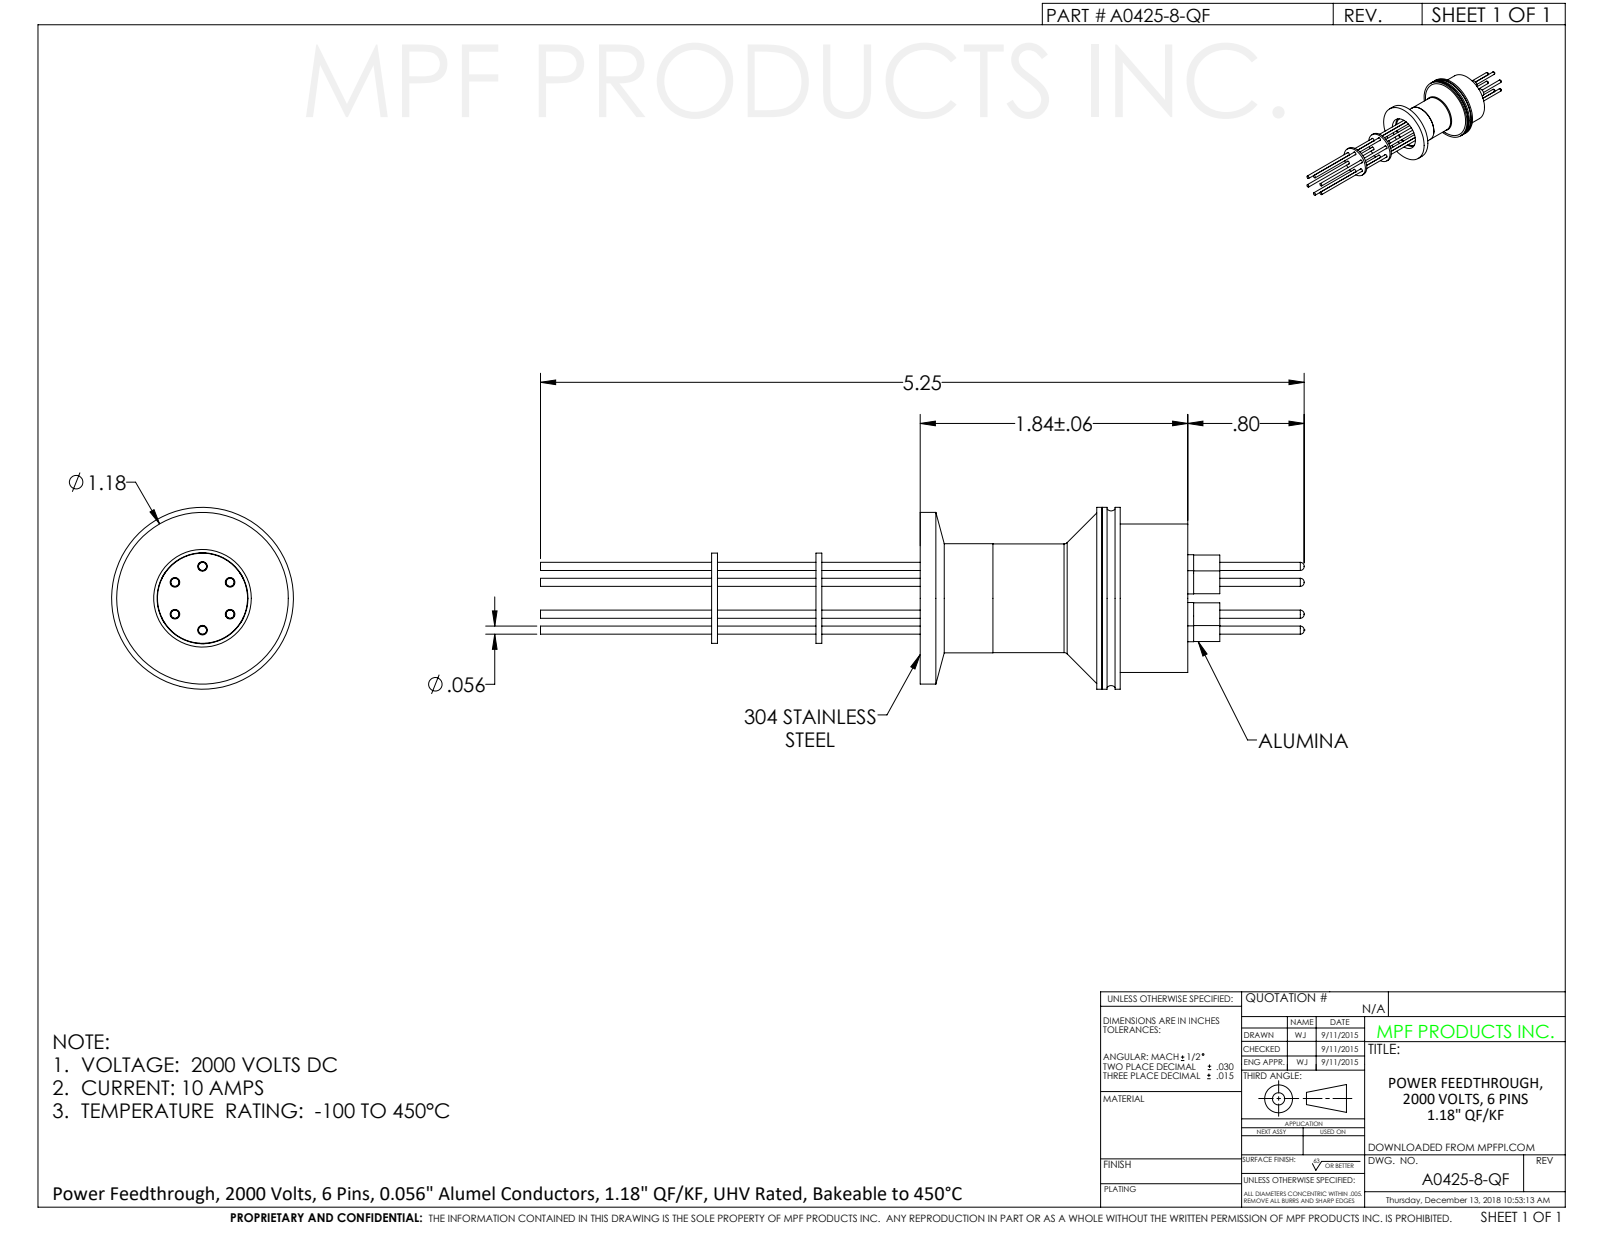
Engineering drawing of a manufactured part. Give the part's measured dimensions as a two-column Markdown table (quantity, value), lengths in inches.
| quantity | value |
| --- | --- |
| part name | A0425-8-QF |
| STEP written by | SolidWorks 2012 (CONFIG_CONTROL_DESIGN) |
| units | inches |
| bodies | 1 solid, 223 faces (49 planar, 132 cylindrical, 42 other) |
| overall size | 5.25 × 1.25 × 1.25 |
| volume | 0.537 in³ |
| surface area | 22.39 in² |
| round holes (diameter × count) | 0.625 × 1, 0.675 × 1, 0.683 × 1, 0.94 × 1, 0.96 × 1, 0.97 × 1 |
| round bosses / shafts (diameter × count) | 0.187 × 6, 0.171 × 6, 0.056 × 6, 1.25 × 1, 1.18 × 1, 1.02 × 1, 0.957 × 1, 0.75 × 1 |
| main face-to-face distances | 1.805, 0.04, 0.517, 1.755, 0.05, 0.43, 1.375, 0.38, 1.431, 2.806 |
| hole center spacings | 0.19, 0.269, 0.269, 0.38, 0.187, 0.193 |
